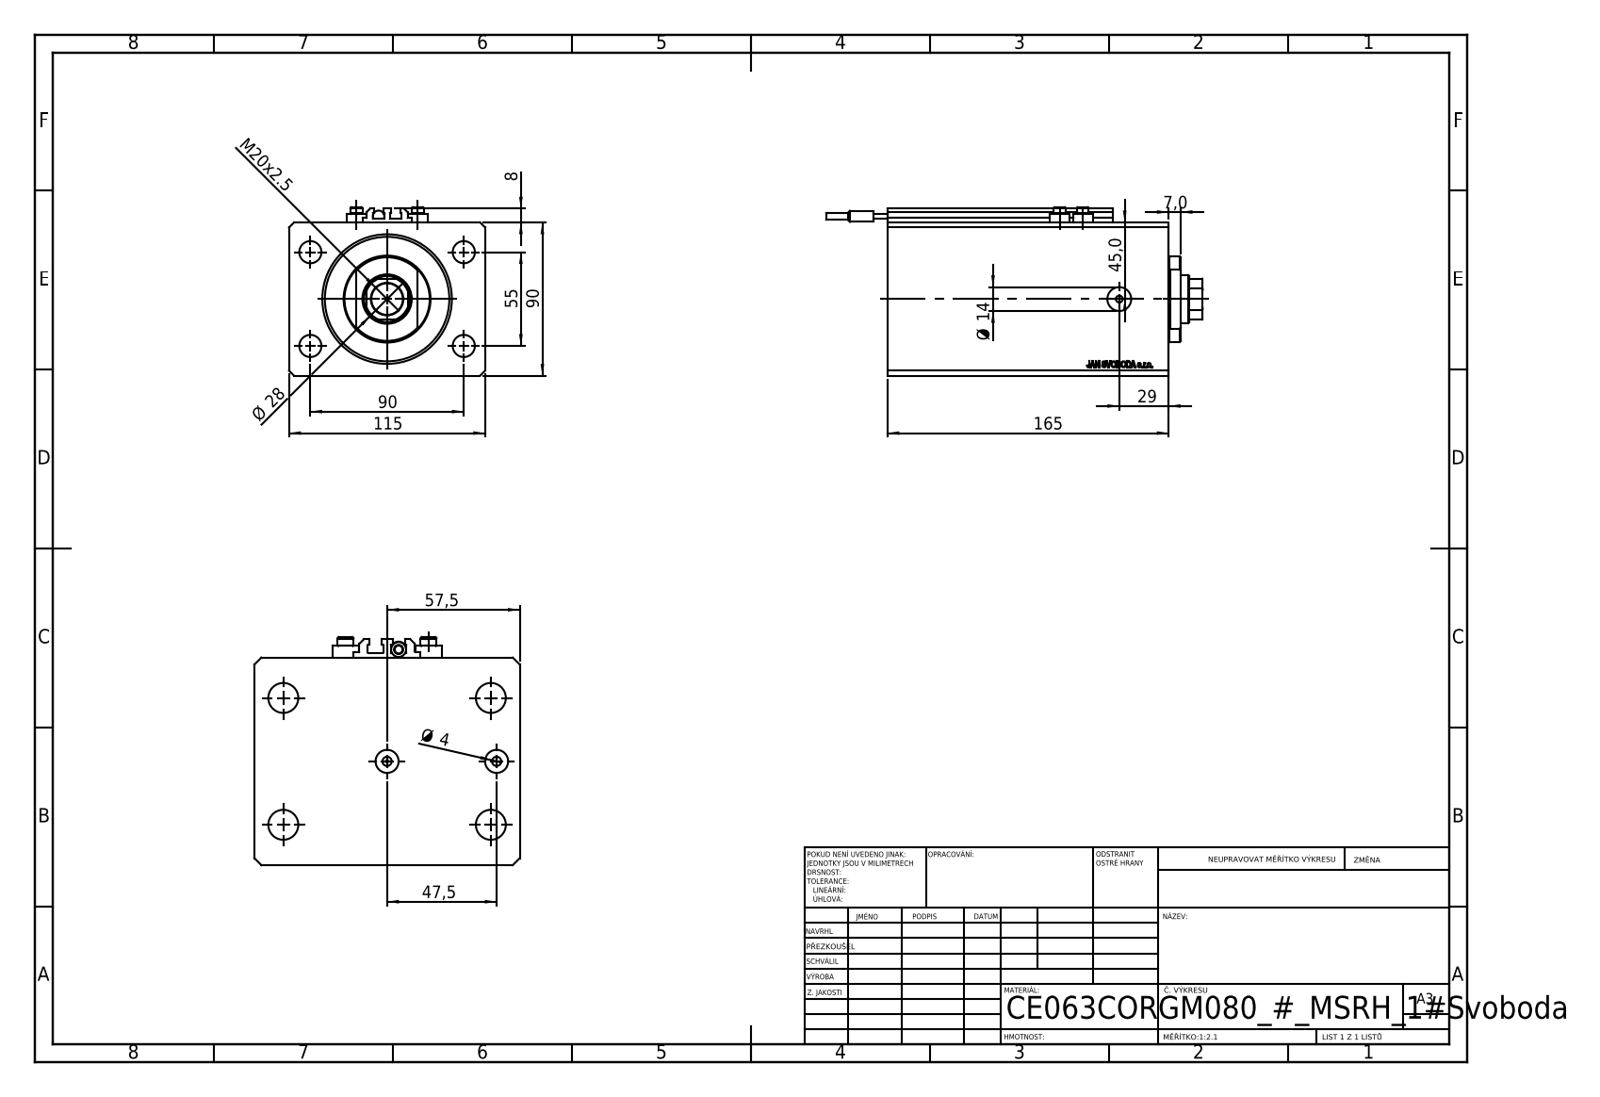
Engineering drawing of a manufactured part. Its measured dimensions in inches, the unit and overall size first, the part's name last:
Units: inches
Overall size (bounding box): 8.701 × 4.528 × 3.898
Round holes (diameter × count): ⌀0.157 ×8, ⌀0.512 ×4, ⌀0.394 ×2, ⌀0.551 ×2, ⌀0.049 ×1, ⌀0.728 ×1, ⌀1.102 ×1, ⌀2.48 ×1, ⌀2.992 ×1
Round bosses / shafts (diameter × count): ⌀0.457 ×4, ⌀0.276 ×4, ⌀1.969 ×1, ⌀0.268 ×1, ⌀0.256 ×1, ⌀0.157 ×1
Partial cylindrical surfaces — rounded edges, fillets, slot ends (radius × count): R0.008 ×10, R0.531 ×1
Main face-to-face distances: 3.543, 4.528, 6.496, 0.705, 5.791, 0.787, 5.709, 5.004, 2.559, 3.937
Hole centre spacings: 2.076, 0.535, 1.087, 1.417, 1.515, 2.165, 3.543, 3.799
Volume: 88.12 in³ · Surface area: 320.4 in²
Bodies: 9 solids, 1064 faces (520 planar, 94 cylindrical, 450 other)
Part name (STEP PRODUCT): V250CE_VC_C; SWITCH_V250CE; V250CE_C_VCP; V250CE_C_Body (+1 more)
STEP written by: SolidWorks 2019 (CONFIG_CONTROL_DESIGN)
